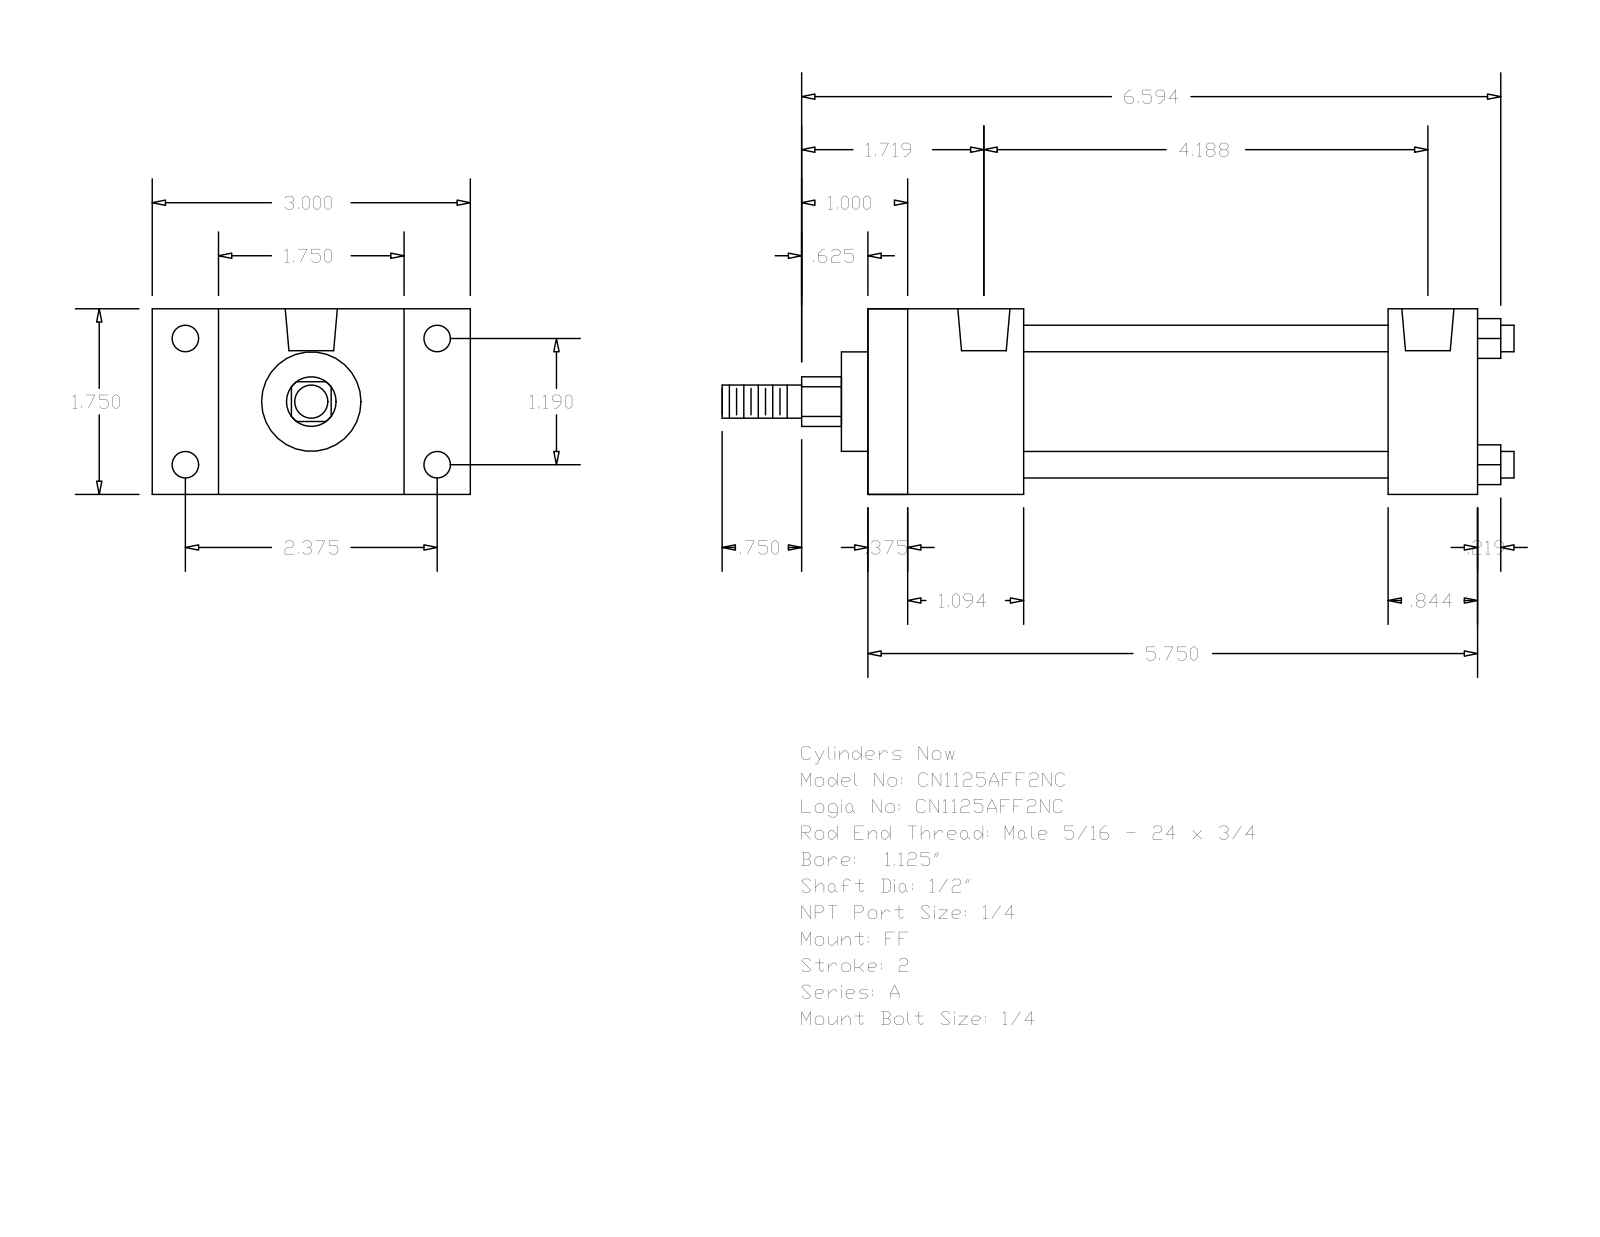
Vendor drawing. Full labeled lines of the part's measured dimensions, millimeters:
Part name (STEP PRODUCT): A_FF__0112_0.5
STEP written by: GSSL Pune (CONFIG_CONTROL_DESIGN)
Units: millimetres
Bodies: 0 solids, 92 faces (64 planar, 28 cylindrical, 0 other)
Overall size (bounding box): 189.71 × 76.2 × 44.45
Round holes (diameter × count): ⌀5.56 ×4, ⌀6.35 ×4, ⌀12.49 ×2
Round bosses / shafts (diameter × count): ⌀6.35 ×4, ⌀31.88 ×1, ⌀23.81 ×1, ⌀12.7 ×1, ⌀7.94 ×1
Partial cylindrical surfaces — rounded edges, fillets, slot ends (radius × count): R5.94 ×1
Main face-to-face distances: 44.46, 146.05, 9.52, 136.53, 15.87, 124.61, 115.09, 21.44, 37.3, 27.78
Hole centre spacings: 30.22, 60.32, 67.47, 103.19, 1.58, 1.59, 104.77, 104.78
